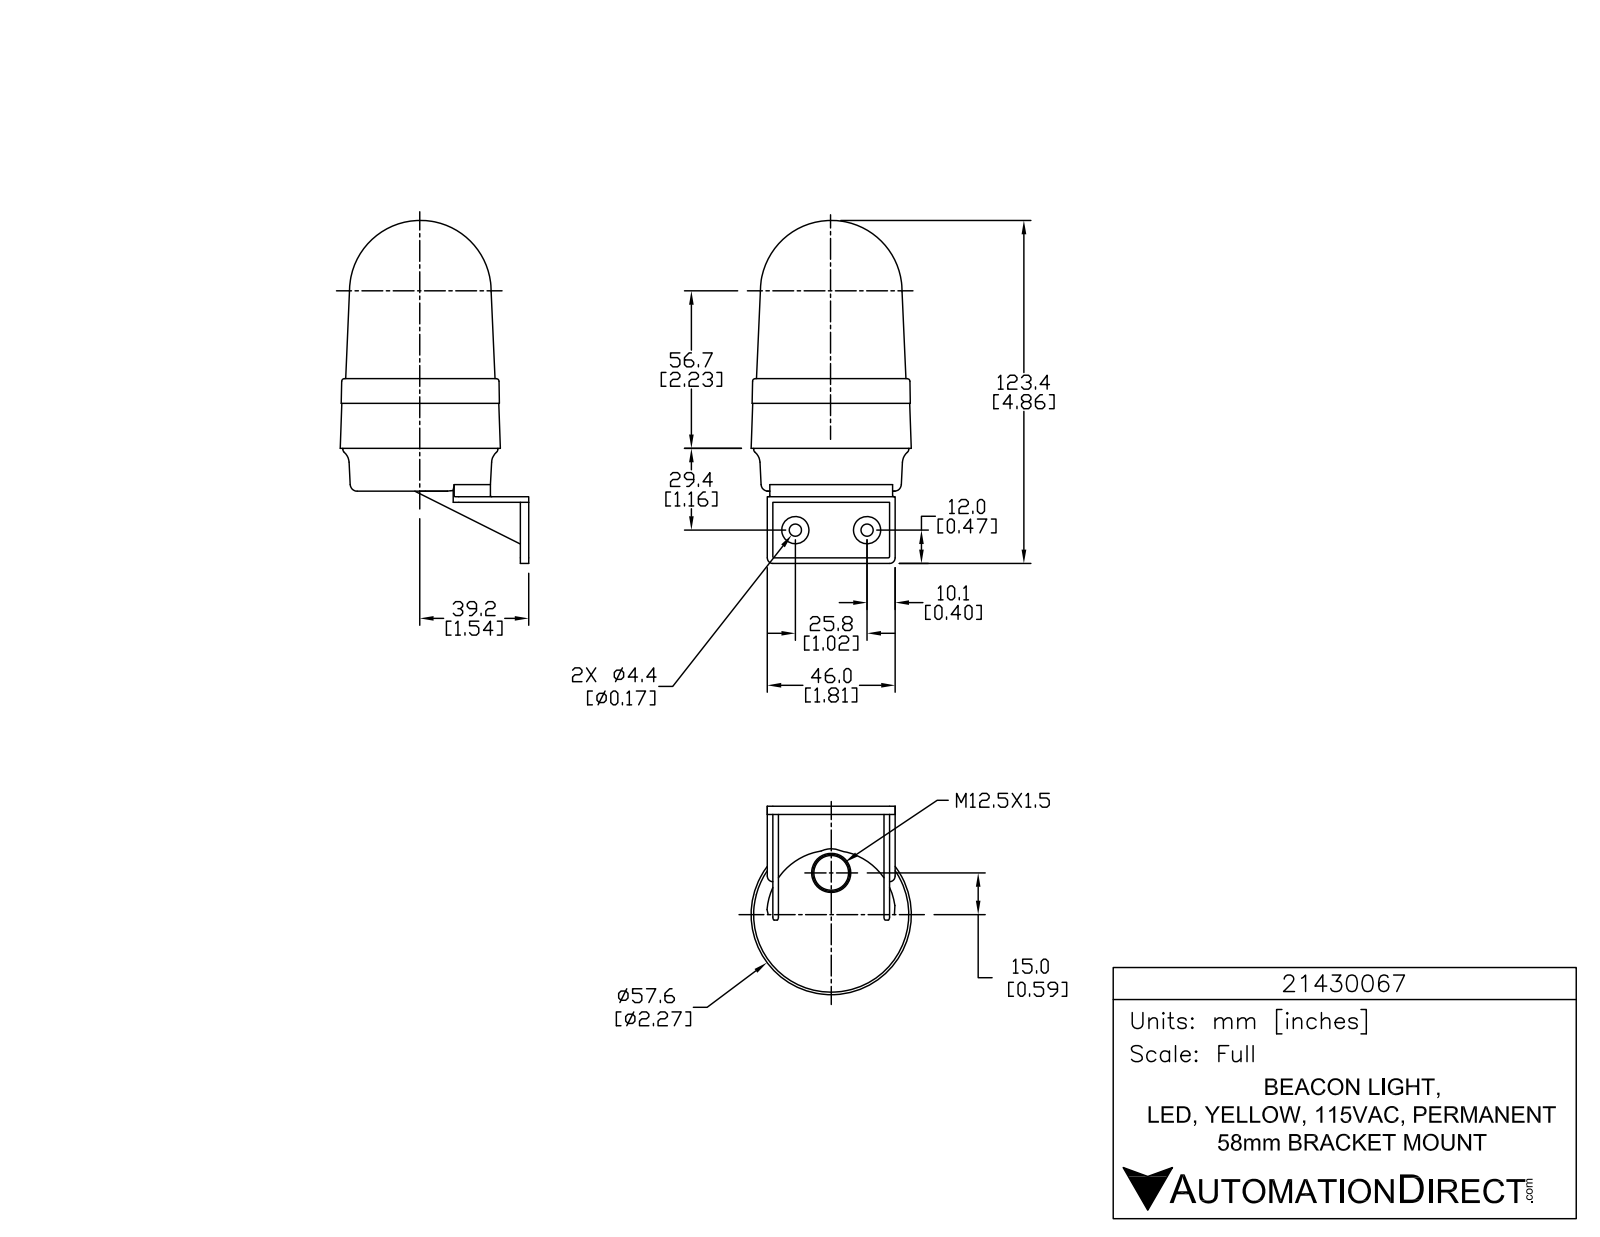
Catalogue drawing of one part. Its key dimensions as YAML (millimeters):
part_name: "21430067"
step_written_by: "SolidWorks 2015 (AUTOMOTIVE_DESIGN)"
units: millimeters
bodies: {solids: 1, faces: 828, planar: 551, cylindrical: 179, other: 98}
overall_size: [123.4, 72.4, 61.1]
volume: 203700
surface_area: 24190
round_holes:
  - {diameter: 1, count: 3}
  - {diameter: 4.4, count: 2}
round_bosses_or_shafts:
  - {diameter: 5.7, count: 3}
  - {diameter: 1.4, count: 3}
  - {diameter: 9.8, count: 2}
  - {diameter: 55.8, count: 1}
partial_cylinders:
  - {radius: 0.2, count: 6}
  - {radius: 0.2, count: 6}
  - {radius: 0.2, count: 6}
  - {radius: 0.5, count: 6}
  - {radius: 3.3, count: 6}
  - {radius: 2, count: 4}
  - {radius: 0.1, count: 3}
  - {radius: 0.1, count: 3}
face_to_face_distances: [2, 4, 40, 42, 1, 3, 38, 22, 24, 19.4]
hole_center_spacings: [25.8]
